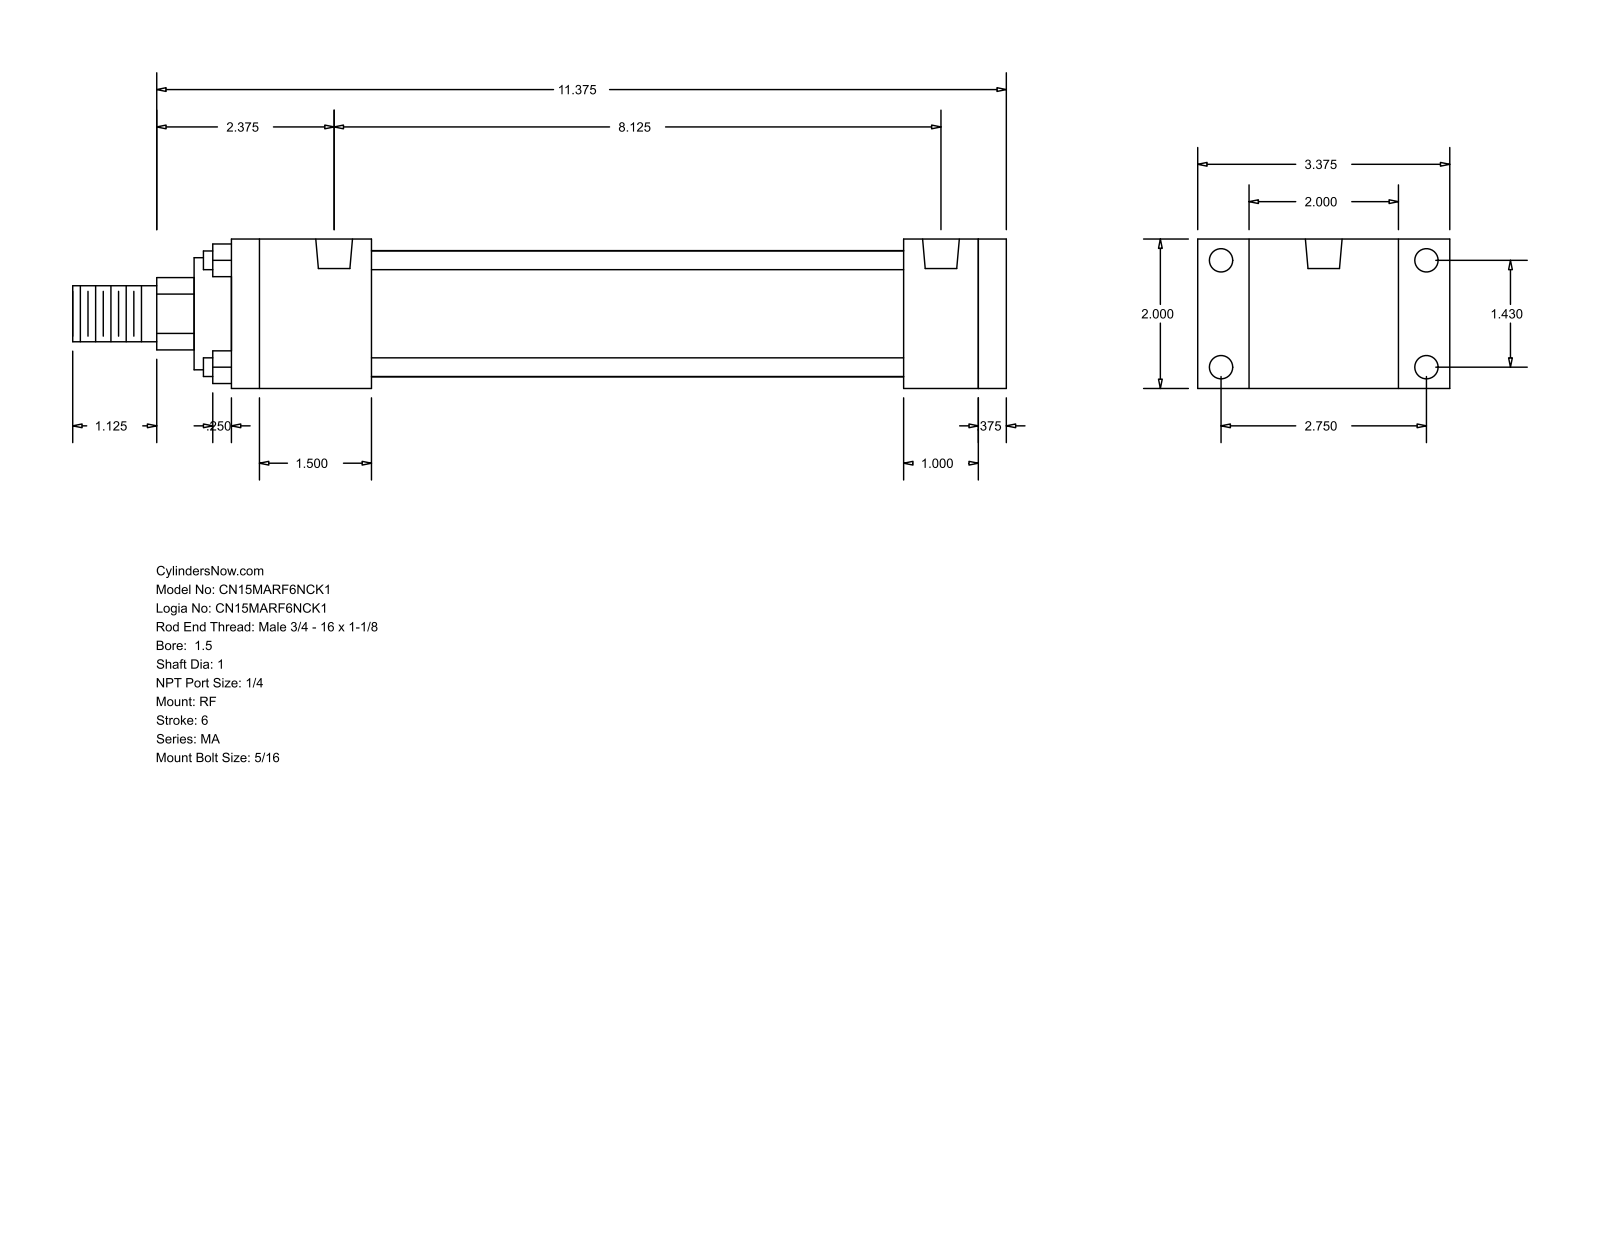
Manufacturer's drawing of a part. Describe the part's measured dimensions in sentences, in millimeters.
The part is named "MA_RF__0150_1". Its 3-D file was written by "GSSL Pune (CONFIG_CONTROL_DESIGN)". It is 0 solids with 92 faces: 64 planar, 28 cylindrical and 0 other. Overall it measures 317.5 by 85.72 by 50.8 millimeters. Round holes: 8 of diameter 7.94, 2 of diameter 12.49. Round bosses or shafts: 4 of diameter 6.35, 1 of diameter 42.93, 1 of diameter 38.1, 1 of diameter 25.4, 1 of diameter 19.05. Partial cylindrical surfaces (rounded edges, fillets, slot ends): 1 of radius 12.29. The main face-to-face distances are 50.8, 9.53, 254, 25.4, 263.53, 228.6, 34.93, 47.63, 180.97, 206.37. The hole center spacings are 36.32, 69.84, 78.72, 206.37.
